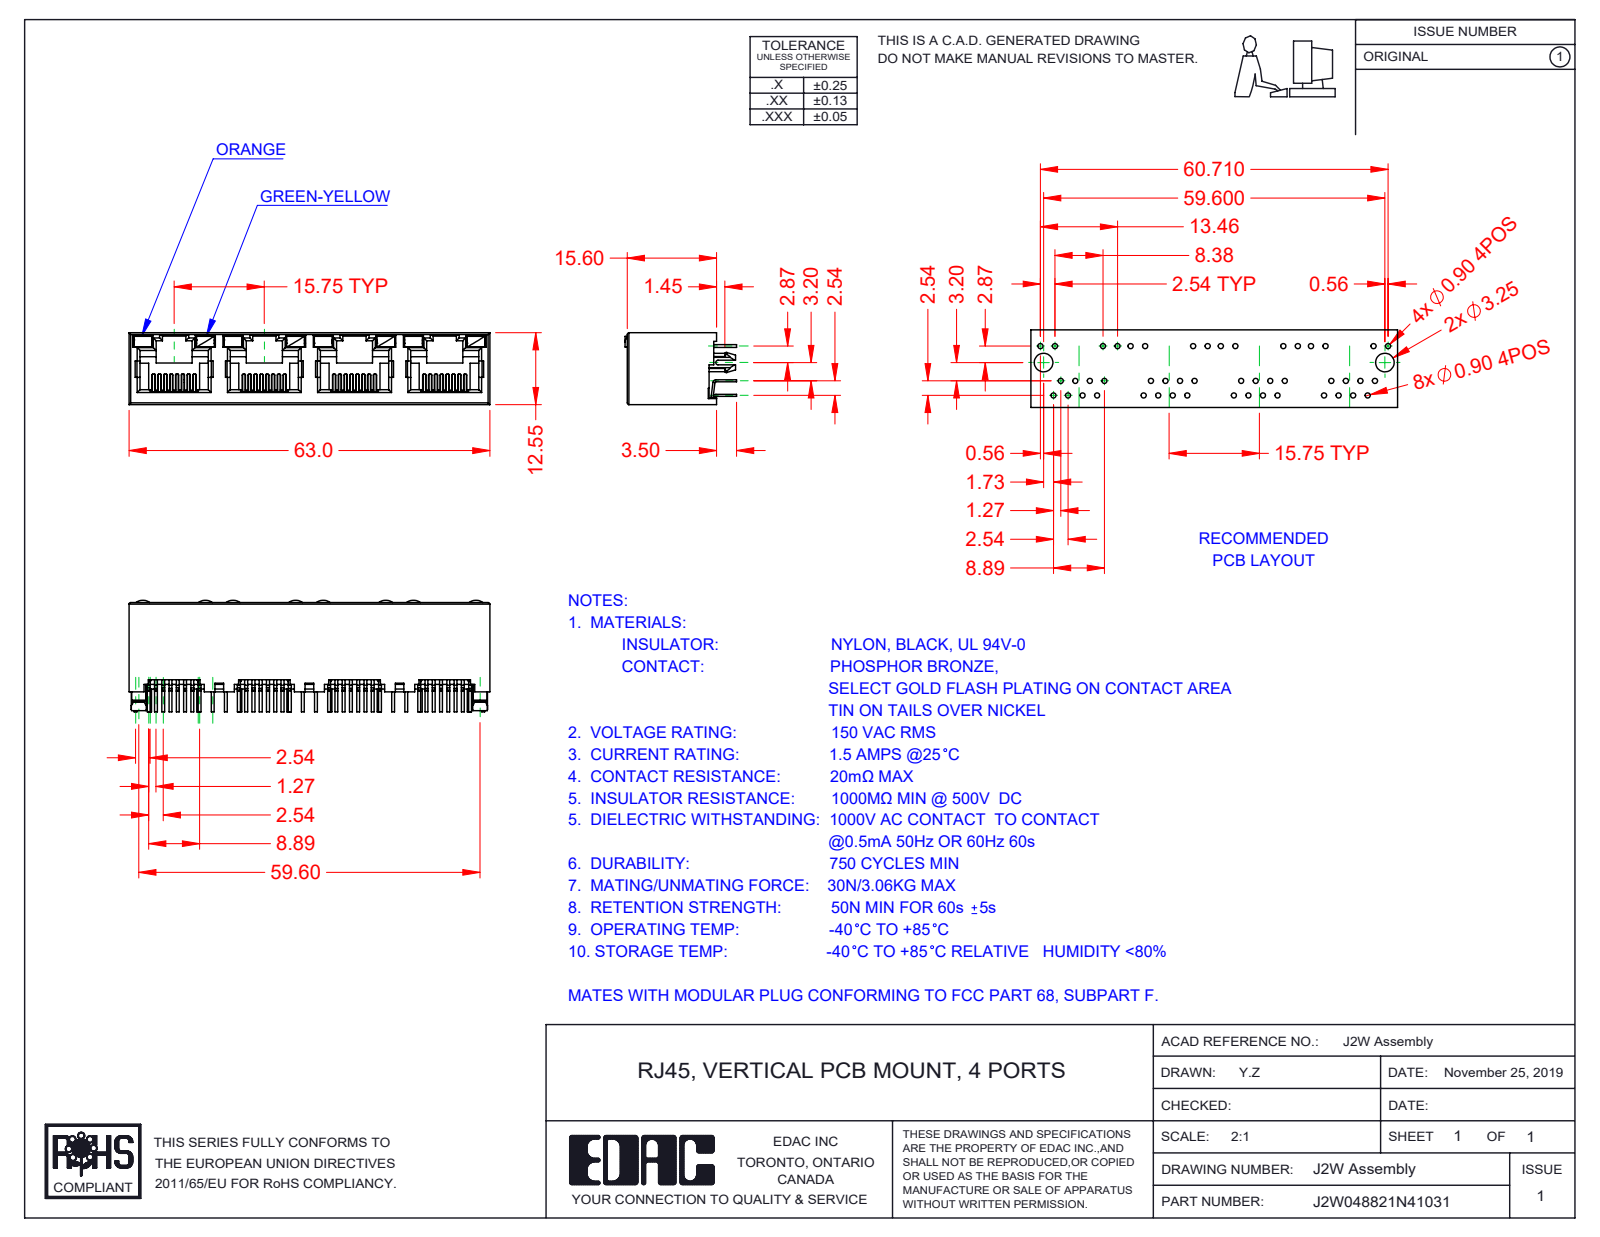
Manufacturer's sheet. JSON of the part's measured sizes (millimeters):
{"part_name": "J2W048821N45131; 2W LED RH_5-Green-Yellow; 2W Contacts; 2W LED LH_4-Orange (+2 more)", "step_written_by": "SolidWorks 2016 (CONFIG_CONTROL_DESIGN)", "units": "millimeters", "bodies": {"solids": 45, "faces": 3139, "planar": 2600, "cylindrical": 481, "other": 58}, "overall_size": [63, 19.5, 12.55], "volume_mm3": 5335, "surface_area_mm2": 13144, "partial_cylinders_radius": [[0.15, 64], [0.2, 29], [0.5, 28], [0.3, 14], [0.45, 8], [2, 8], [0.25, 2], [1.5, 2]], "face_to_face_distances": [12.55, 11.9, 0.65, 15.75, 0.36, 1.5, 0.78, 0.6, 11.3, 31.5]}
